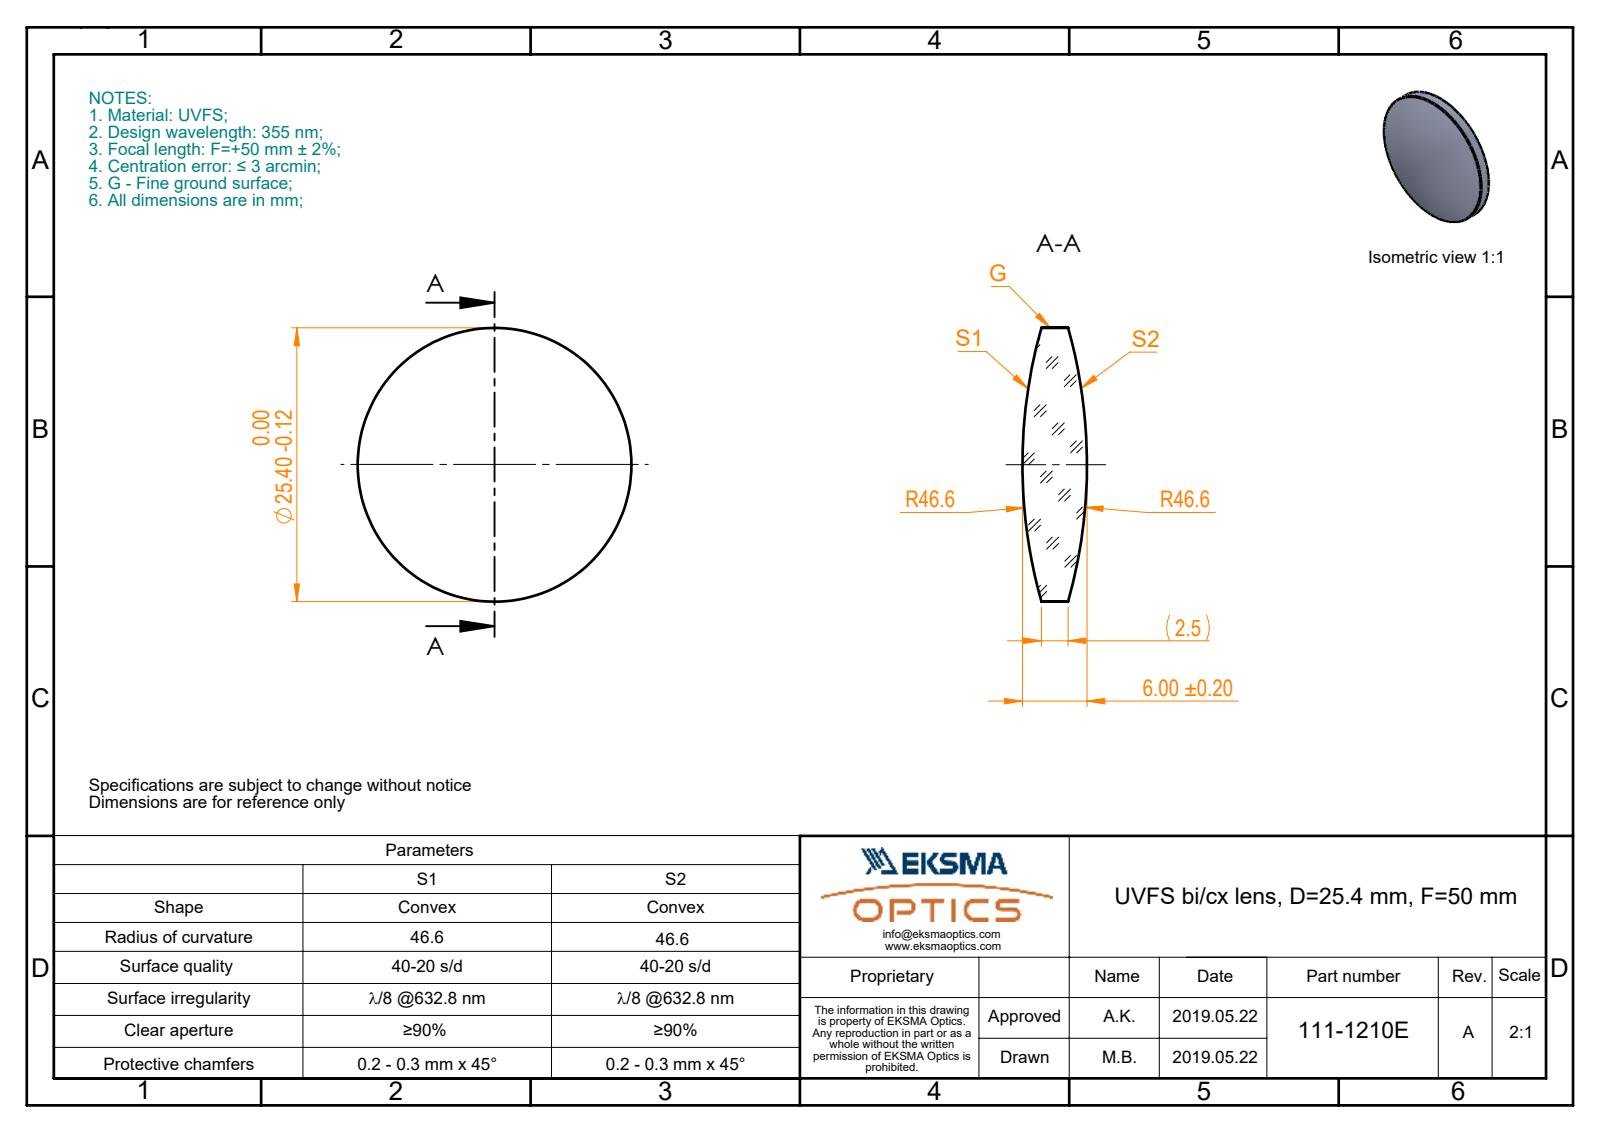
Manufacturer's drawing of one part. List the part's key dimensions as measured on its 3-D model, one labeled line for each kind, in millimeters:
Part name (STEP PRODUCT): 111-1210E UVFS bi-cx 25.4 F50
STEP written by: SolidWorks 2017 (CONFIG_CONTROL_DESIGN)
Units: millimetres
Bodies: 1 solid, 6 faces (0 planar, 2 cylindrical, 4 other)
Overall size (bounding box): 25.4 × 25.4 × 6
Volume: 2 153 mm³ · Surface area: 1 230 mm²
Round bosses / shafts (diameter × count): ⌀25.4 ×1
